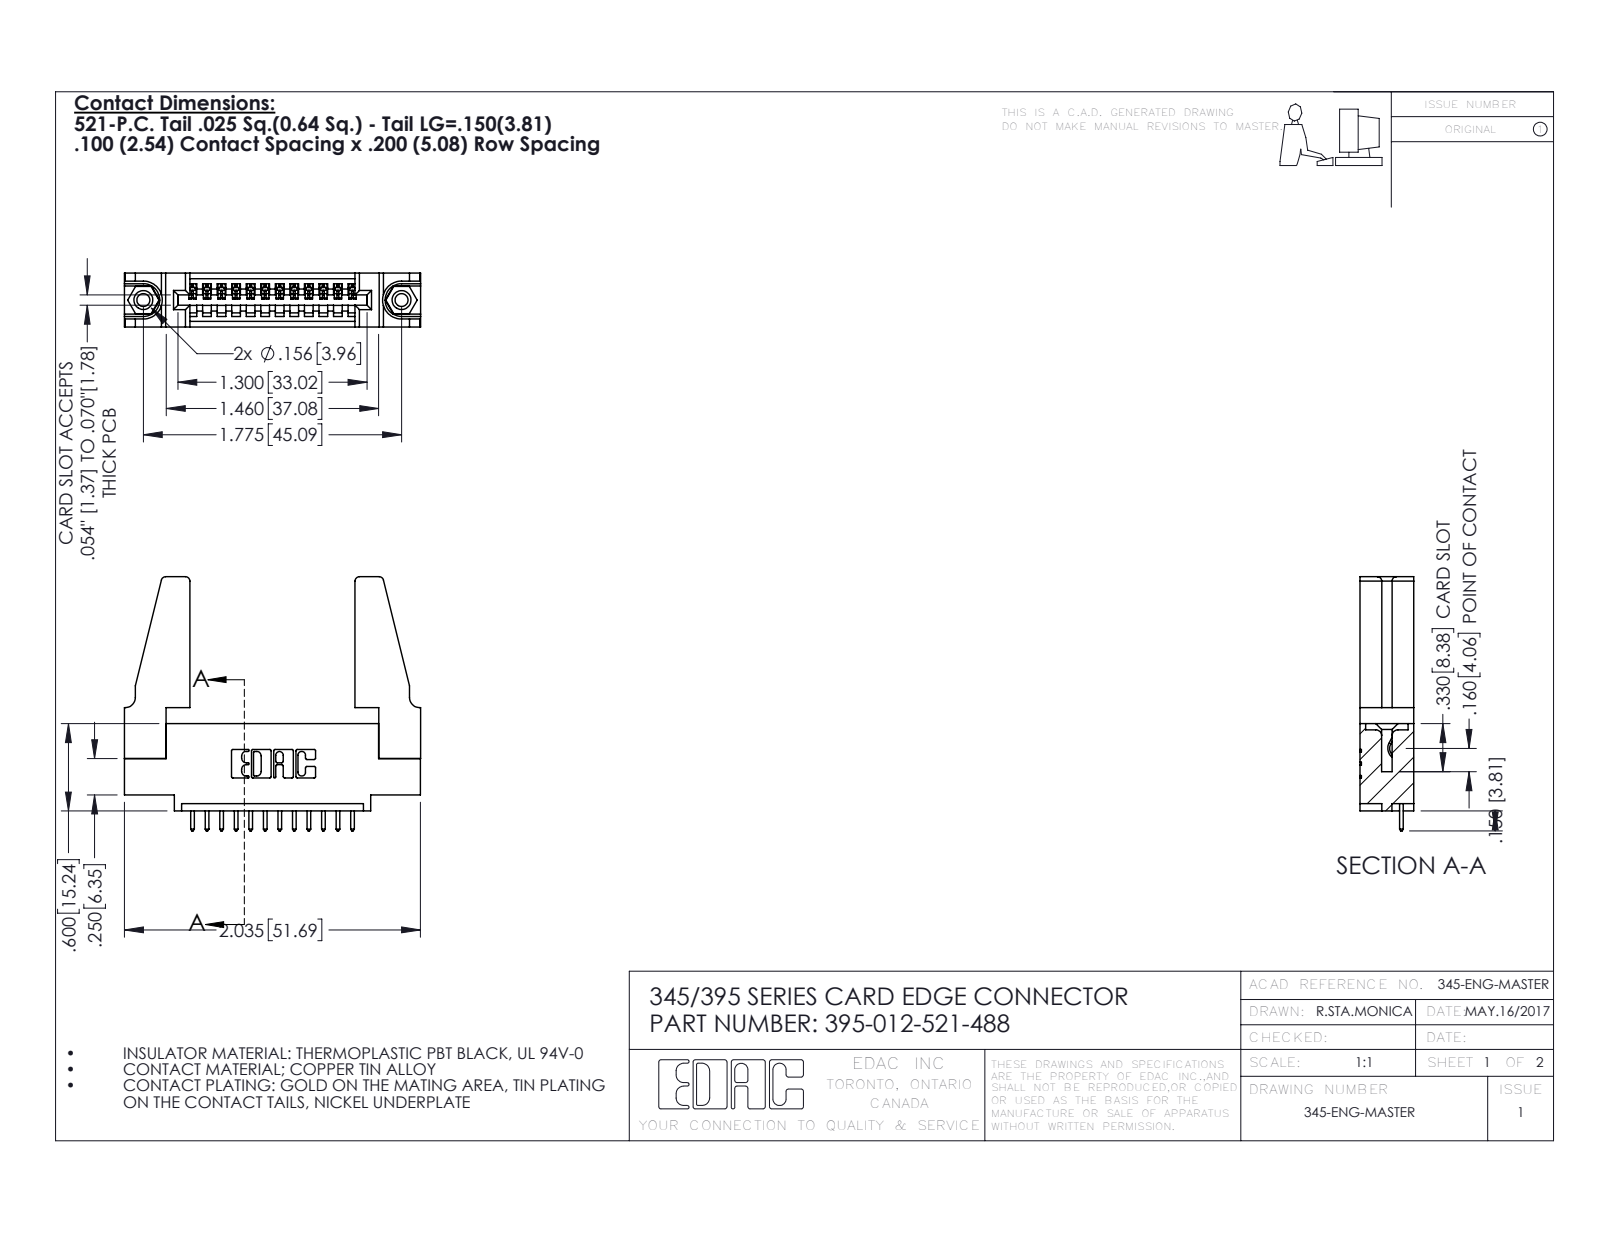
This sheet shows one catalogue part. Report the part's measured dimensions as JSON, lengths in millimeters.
{"part_name": "395-012-521-488; 345-250-001_345-250-001-102; 345-220-078_345-220-088; 345-292-001_345-293-121 (+1 more)", "step_written_by": "SolidWorks 2016 (CONFIG_CONTROL_DESIGN)", "units": "millimeters", "bodies": {"solids": 17, "faces": 950, "planar": 636, "cylindrical": 298, "other": 16}, "overall_size": [51.7, 44.4, 9.4], "volume_mm3": 7820, "surface_area_mm2": 8729, "round_holes": [[2.3, 2], [3.2, 2], [4, 2], [1.6, 1]], "round_bosses_or_shafts": [[3.9, 2]], "partial_cylinders_radius": [[0.2, 24], [0.3, 24], [0.3, 22], [0.8, 8], [0.2, 6], [0.8, 6], [0.7, 3], [0.8, 2]], "face_to_face_distances": [9.4, 1.8, 7.6, 5.1, 2.5, 6.9, 0.6, 5.7, 3.8, 3.8], "hole_center_spacings": [6.9, 39.2, 45.1]}
